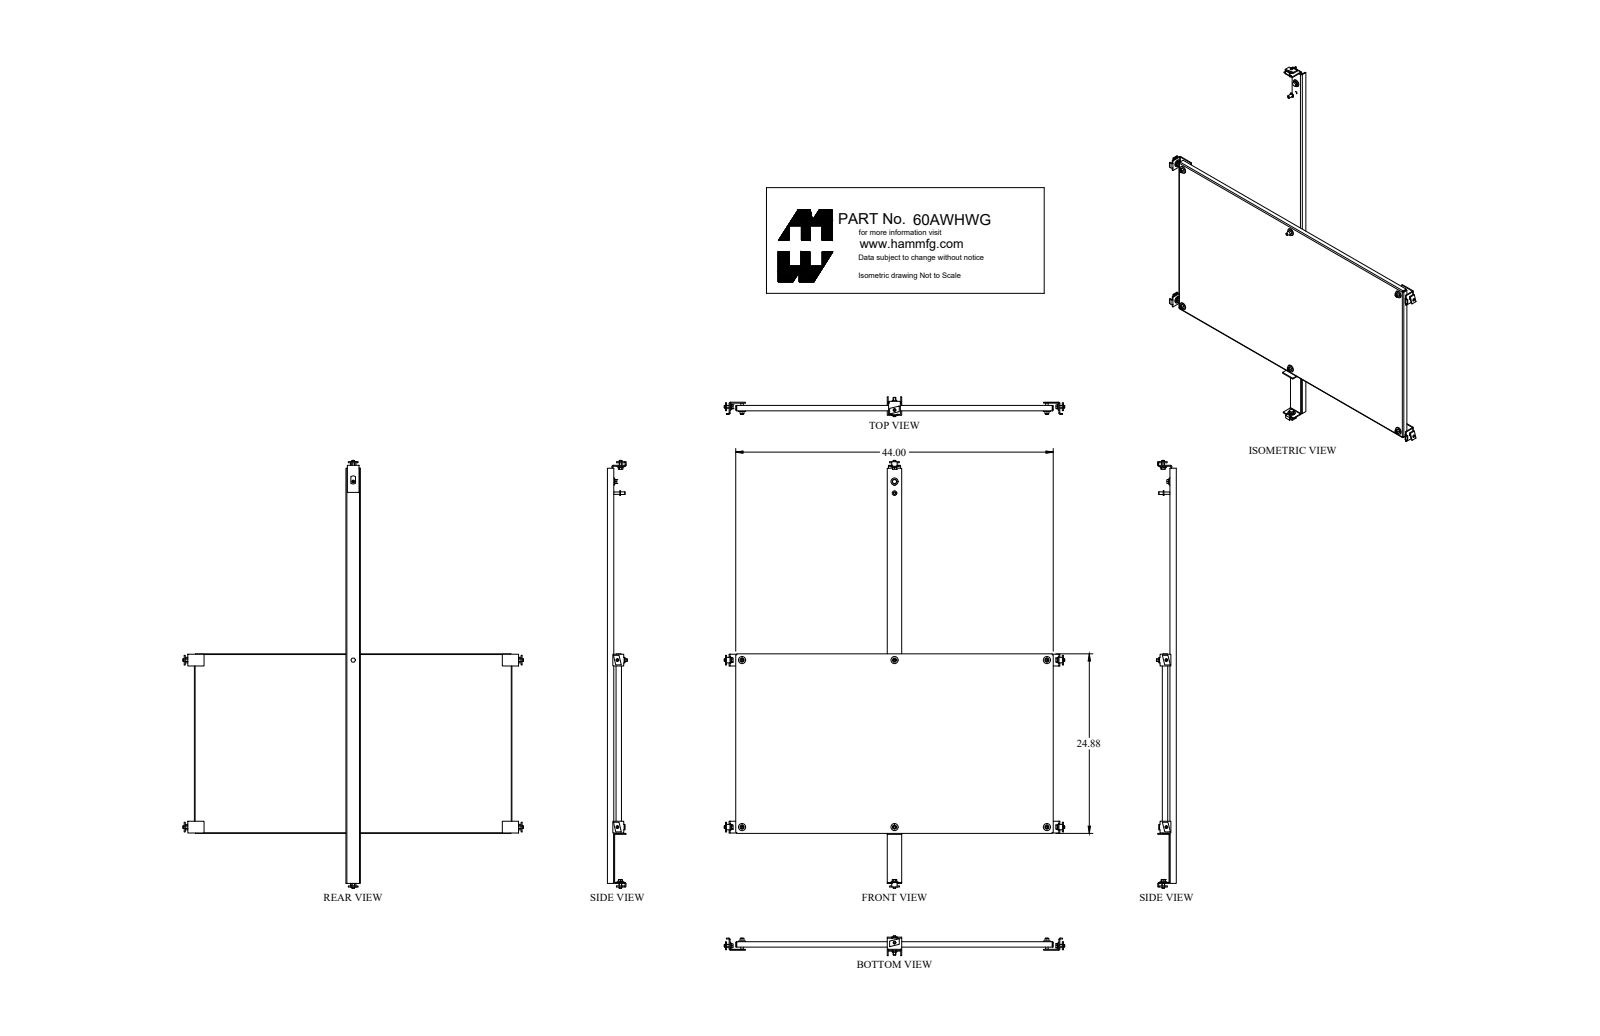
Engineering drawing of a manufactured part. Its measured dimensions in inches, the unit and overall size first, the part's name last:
Units: inches
Overall size (bounding box): 58.906 × 46.582 × 2.593
Round holes (diameter × count): ⌀0.563 ×6, ⌀0.437 ×4, ⌀0.437 ×1, ⌀0.453 ×1
Round bosses / shafts (diameter × count): ⌀0.65 ×6, ⌀0.33 ×6, ⌀0.375 ×4, ⌀0.375 ×2
Partial cylindrical surfaces — rounded edges, fillets, slot ends (radius × count): R0.06 ×11, R0.185 ×11, R0.048 ×4, R0.143 ×4, R0.219 ×2
Main face-to-face distances: 0.095, 0.125, 1.187, 1.062, 0.967, 1.092, 0.125, 24.78, 2, 1.875
Hole centre spacings: 23.125, 21.125, 21.125, 31.321, 31.322, 42.25, 48.165, 0.031
Volume: 143.8 in³ · Surface area: 2 905 in²
Bodies: 14 solids, 305 faces (152 planar, 105 cylindrical, 48 other)
Part name (STEP PRODUCT): 60AWHWG_Default
STEP written by: SolidWorks 2018 (CONFIG_CONTROL_DESIGN)
